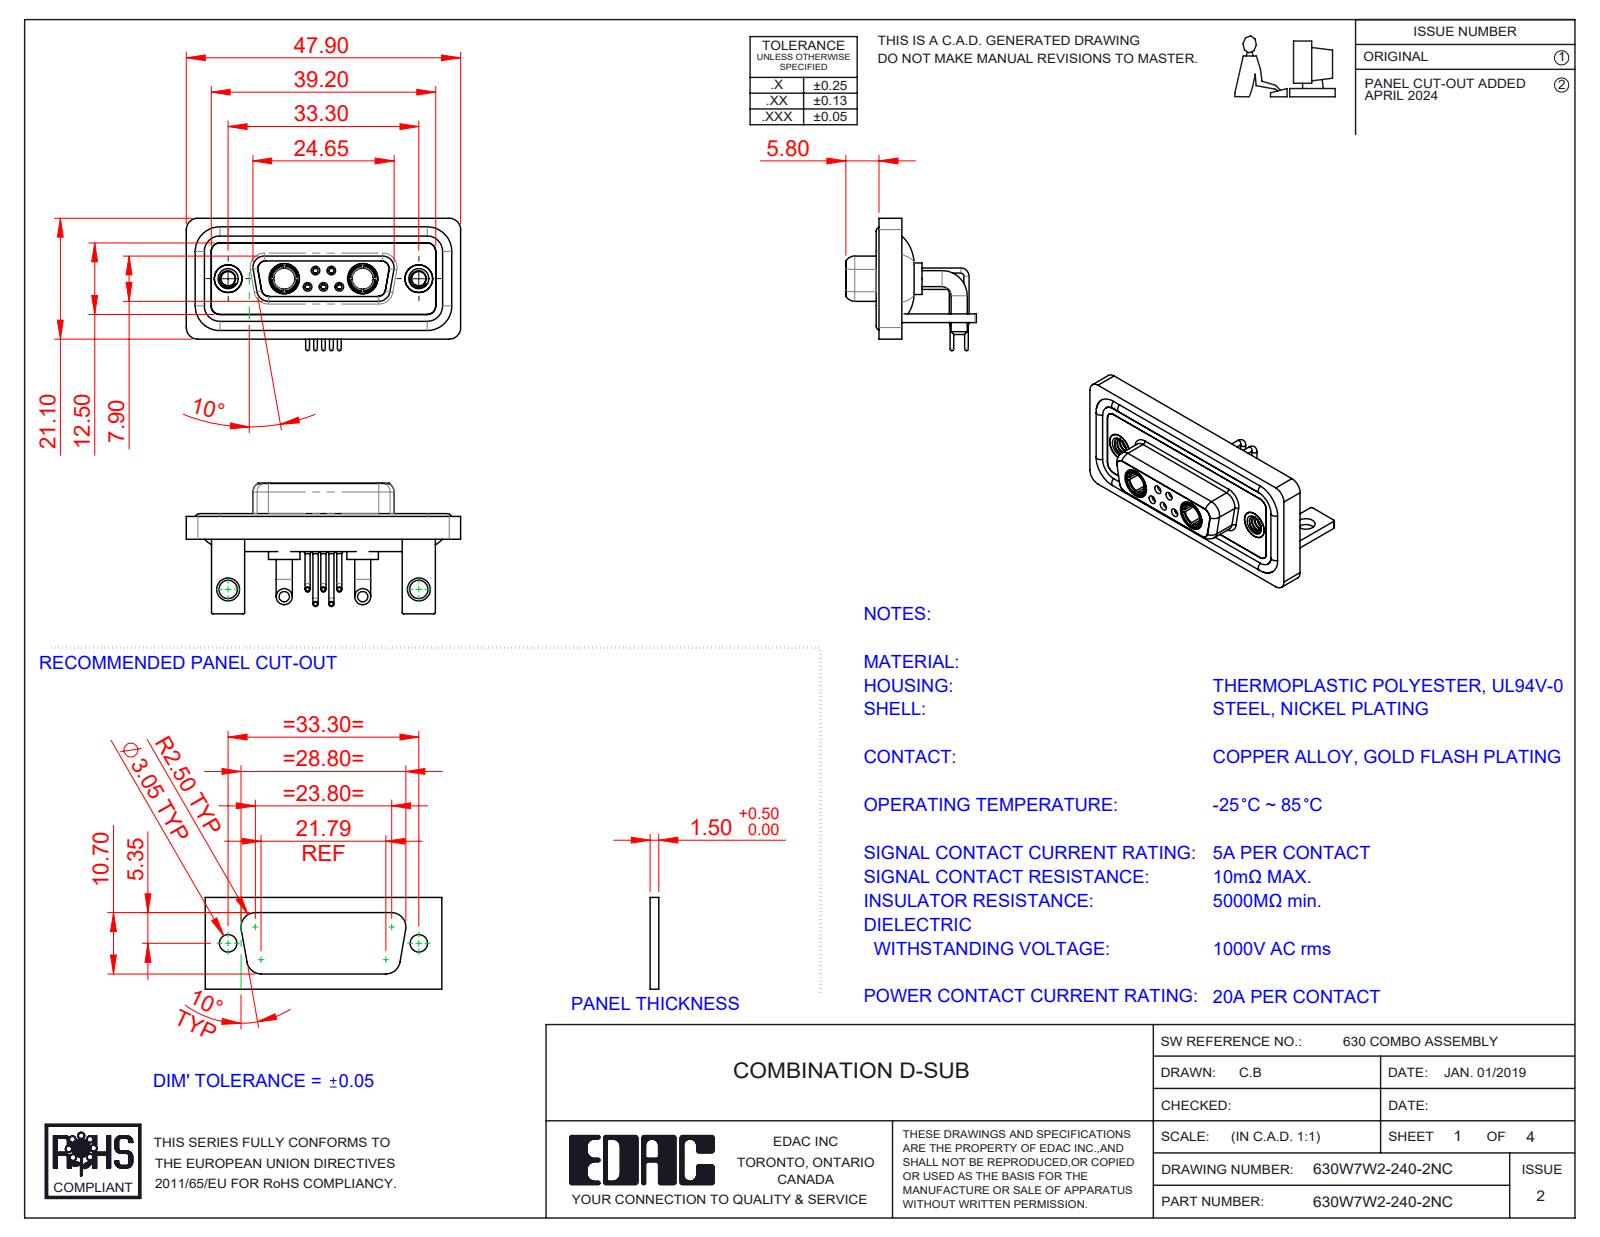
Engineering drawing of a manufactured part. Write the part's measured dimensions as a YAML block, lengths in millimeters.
part_name: "Power Socket_20A RA; 630Combo Contact Row 2_50 Contacts; 630W7W2-240-2NC; 630Combo Stabilizer Bracket_50 Contacts (+6 more)"
step_written_by: "SolidWorks 2023 (CONFIG_CONTROL_DESIGN)"
units: millimeters
bodies: {solids: 18, faces: 849, planar: 258, cylindrical: 375, other: 216}
overall_size: [47.9, 23.12, 22.8]
volume: 6555
surface_area: 10944
round_holes:
  - {diameter: 0.9, count: 5}
  - {diameter: 1.1, count: 5}
  - {diameter: 1.5, count: 5}
  - {diameter: 2, count: 5}
  - {diameter: 4.85, count: 4}
  - {diameter: 1.6, count: 3}
  - {diameter: 1.7, count: 2}
  - {diameter: 2.5, count: 2}
  - {diameter: 3.2, count: 2}
  - {diameter: 3.7, count: 2}
  - {diameter: 4, count: 2}
  - {diameter: 4.05, count: 2}
round_bosses_or_shafts:
  - {diameter: 1.6, count: 6}
  - {diameter: 0.9, count: 5}
  - {diameter: 0.65, count: 5}
  - {diameter: 2.8, count: 4}
  - {diameter: 5.5, count: 2}
  - {diameter: 5.2, count: 2}
  - {diameter: 4.96, count: 2}
  - {diameter: 4.95, count: 2}
partial_cylinders:
  - {radius: 2, count: 21}
  - {radius: 1.5, count: 18}
  - {radius: 0.25, count: 16}
  - {radius: 1.35, count: 12}
  - {radius: 1.6, count: 8}
  - {radius: 0.5, count: 5}
  - {radius: 0.6, count: 4}
  - {radius: 0.65, count: 4}
face_to_face_distances: [0.4, 2.9, 1.5, 1.8, 3.7, 1.1, 4.1, 1.6, 2.5, 1.4]
hole_center_spacings: [3.16, 2.77, 9.8, 23.5, 33.3, 4.31, 4.33, 5.03]
